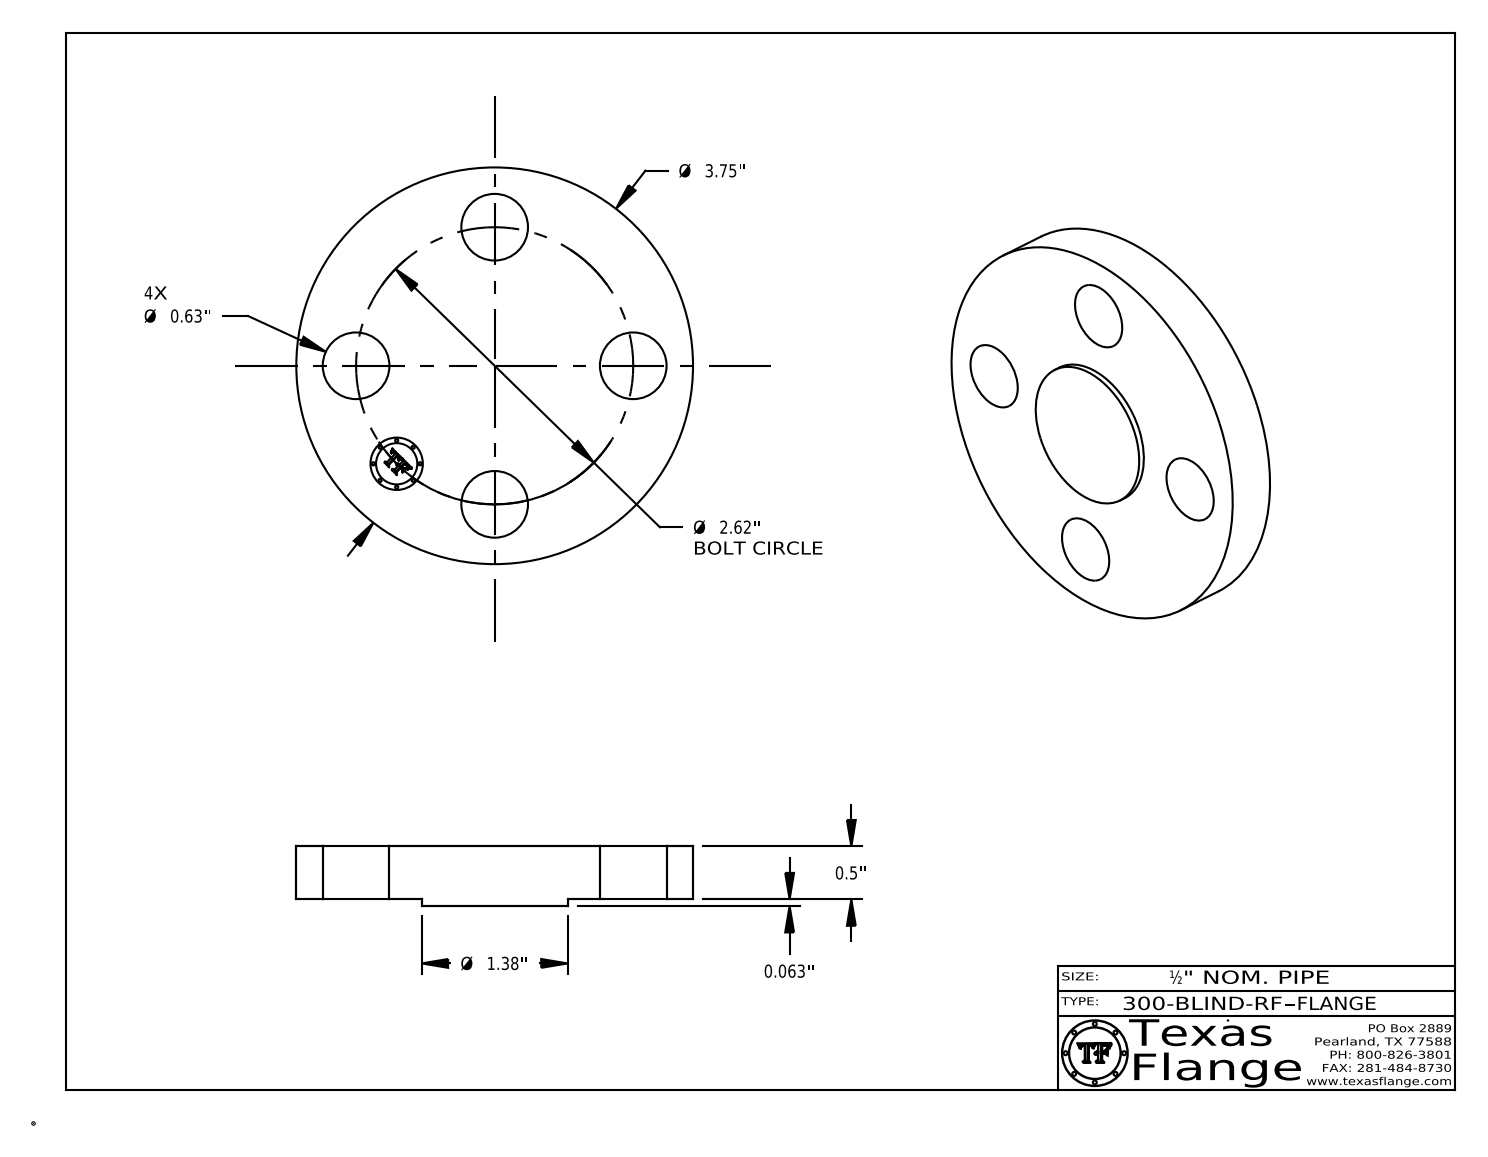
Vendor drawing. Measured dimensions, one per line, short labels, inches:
name: 300-BLIND-RF
written by: CATIA V5 STEP AP214 (AUTOMOTIVE_DESIGN)
unit: in
bodies: 1 solid, 400 faces (368 planar, 32 cylindrical, 0 other)
size: 3.75 × 3.75 × 0.563
volume: 4.991 in³; area: 29.81 in²
holes: 4× ⌀0.63, 1× ⌀0.495
bosses: 8× ⌀0.03, 1× ⌀3.75, 1× ⌀1.38, 1× ⌀0.39
face distances: 0.5, 0.063, 0.563, 0.548, 0.485, 0.015, 0.148, 0.144, 0.027, 0.096
hole spacings: 1.852, 1.003, 2.42, 2.62
